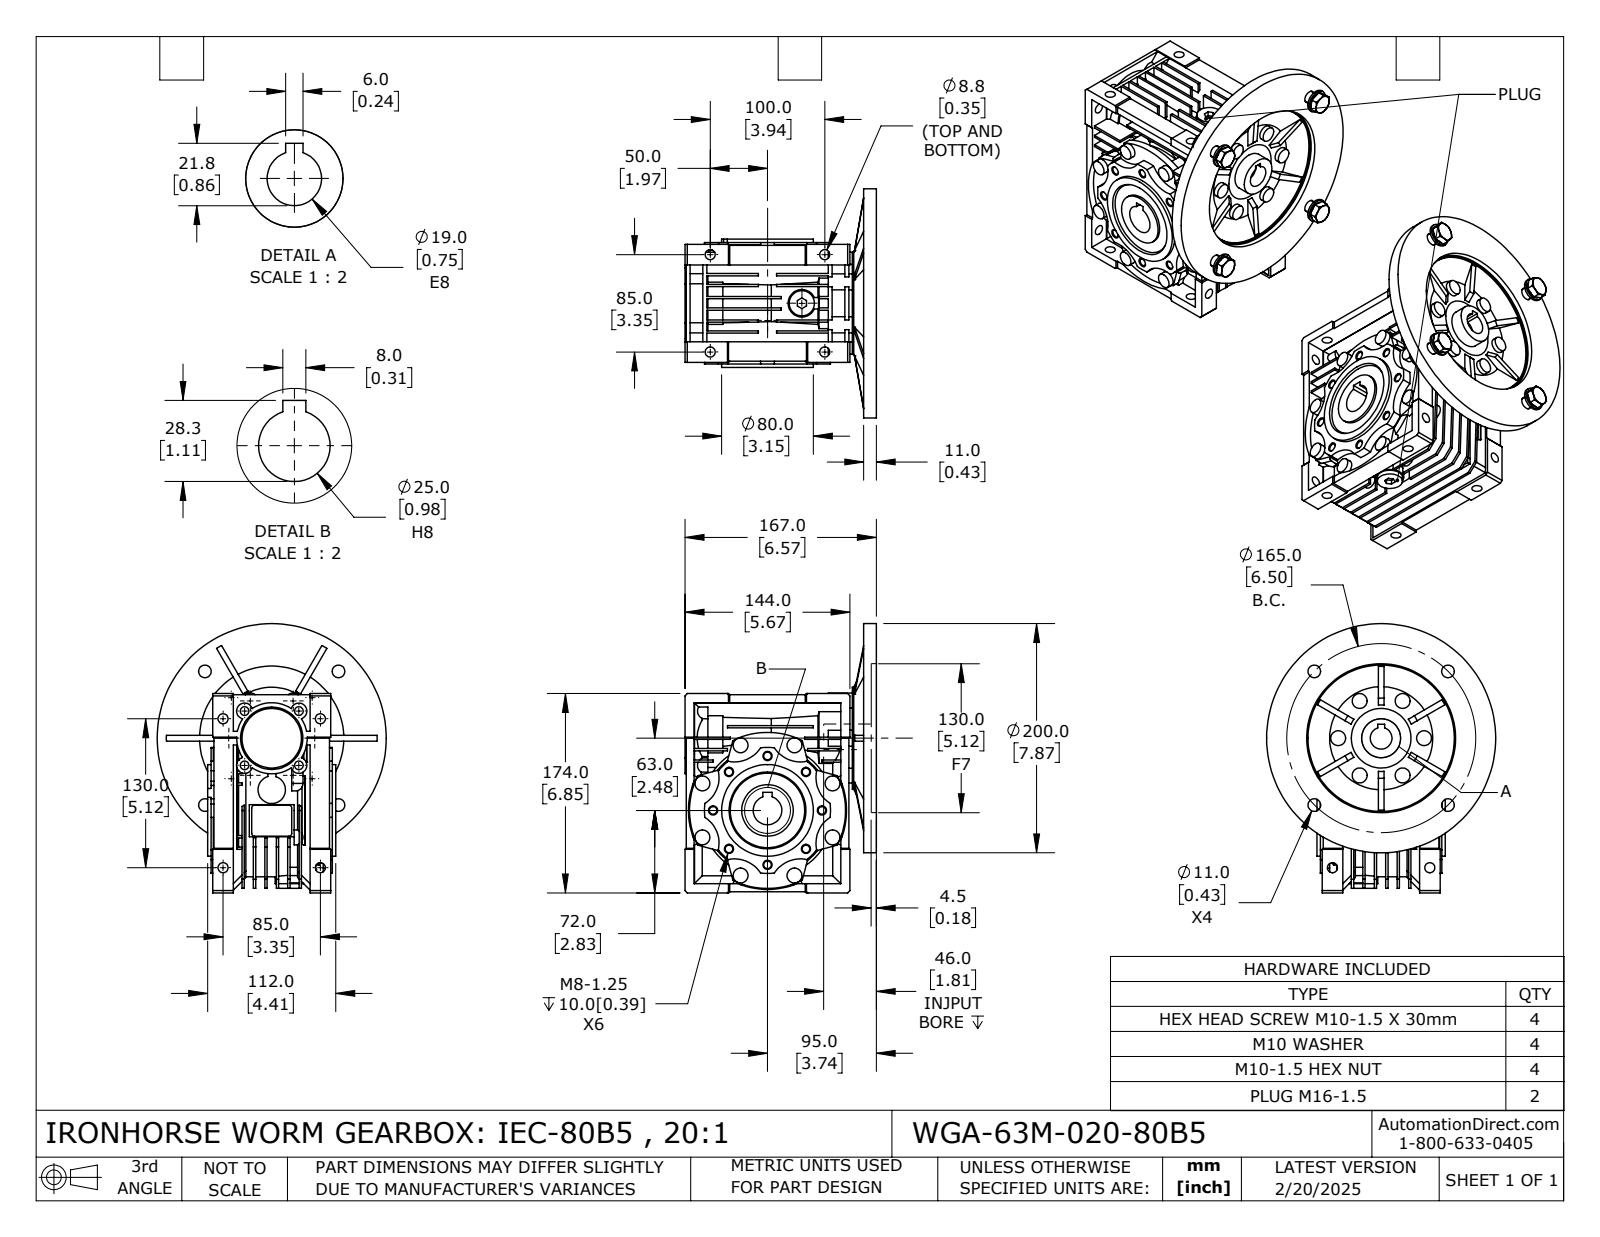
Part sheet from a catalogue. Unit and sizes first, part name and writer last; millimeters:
Units: millimetres
Overall size (bounding box): 235 × 200 × 183.43
Round holes (diameter × count): ⌀6.65 ×8, ⌀8.78 ×8, ⌀7.56 ×4, ⌀8.5 ×4, ⌀10 ×4, ⌀10.5 ×4, ⌀11 ×4, ⌀14.5 ×2, ⌀19 ×1, ⌀20 ×1, ⌀25 ×1, ⌀34 ×1
Round bosses / shafts (diameter × count): ⌀13 ×14, ⌀20 ×4, ⌀16 ×4, ⌀24 ×3, ⌀22 ×2, ⌀15.8 ×2, ⌀13.7 ×2, ⌀200 ×1
Partial cylindrical surfaces — rounded edges, fillets, slot ends (radius × count): R7 ×10, R27 ×8, R2.5 ×4, R8.35 ×1, R29.5 ×1, R30.5 ×1, R42 ×1, R46 ×1
Main face-to-face distances: 10, 8, 20, 2, 11, 30, 12, 7, 40, 18
Hole centre spacings: 36.36, 47.5, 67.18, 87.77, 89.05, 33.5, 47.38, 49
Volume: 2 032 000 mm³ · Surface area: 401 437 mm²
Bodies: 20 solids, 1529 faces (897 planar, 394 cylindrical, 238 other)
Part name (STEP PRODUCT): WGA-63M-020-80B5
STEP written by: SolidWorks 2024 (CONFIG_CONTROL_DESIGN)
